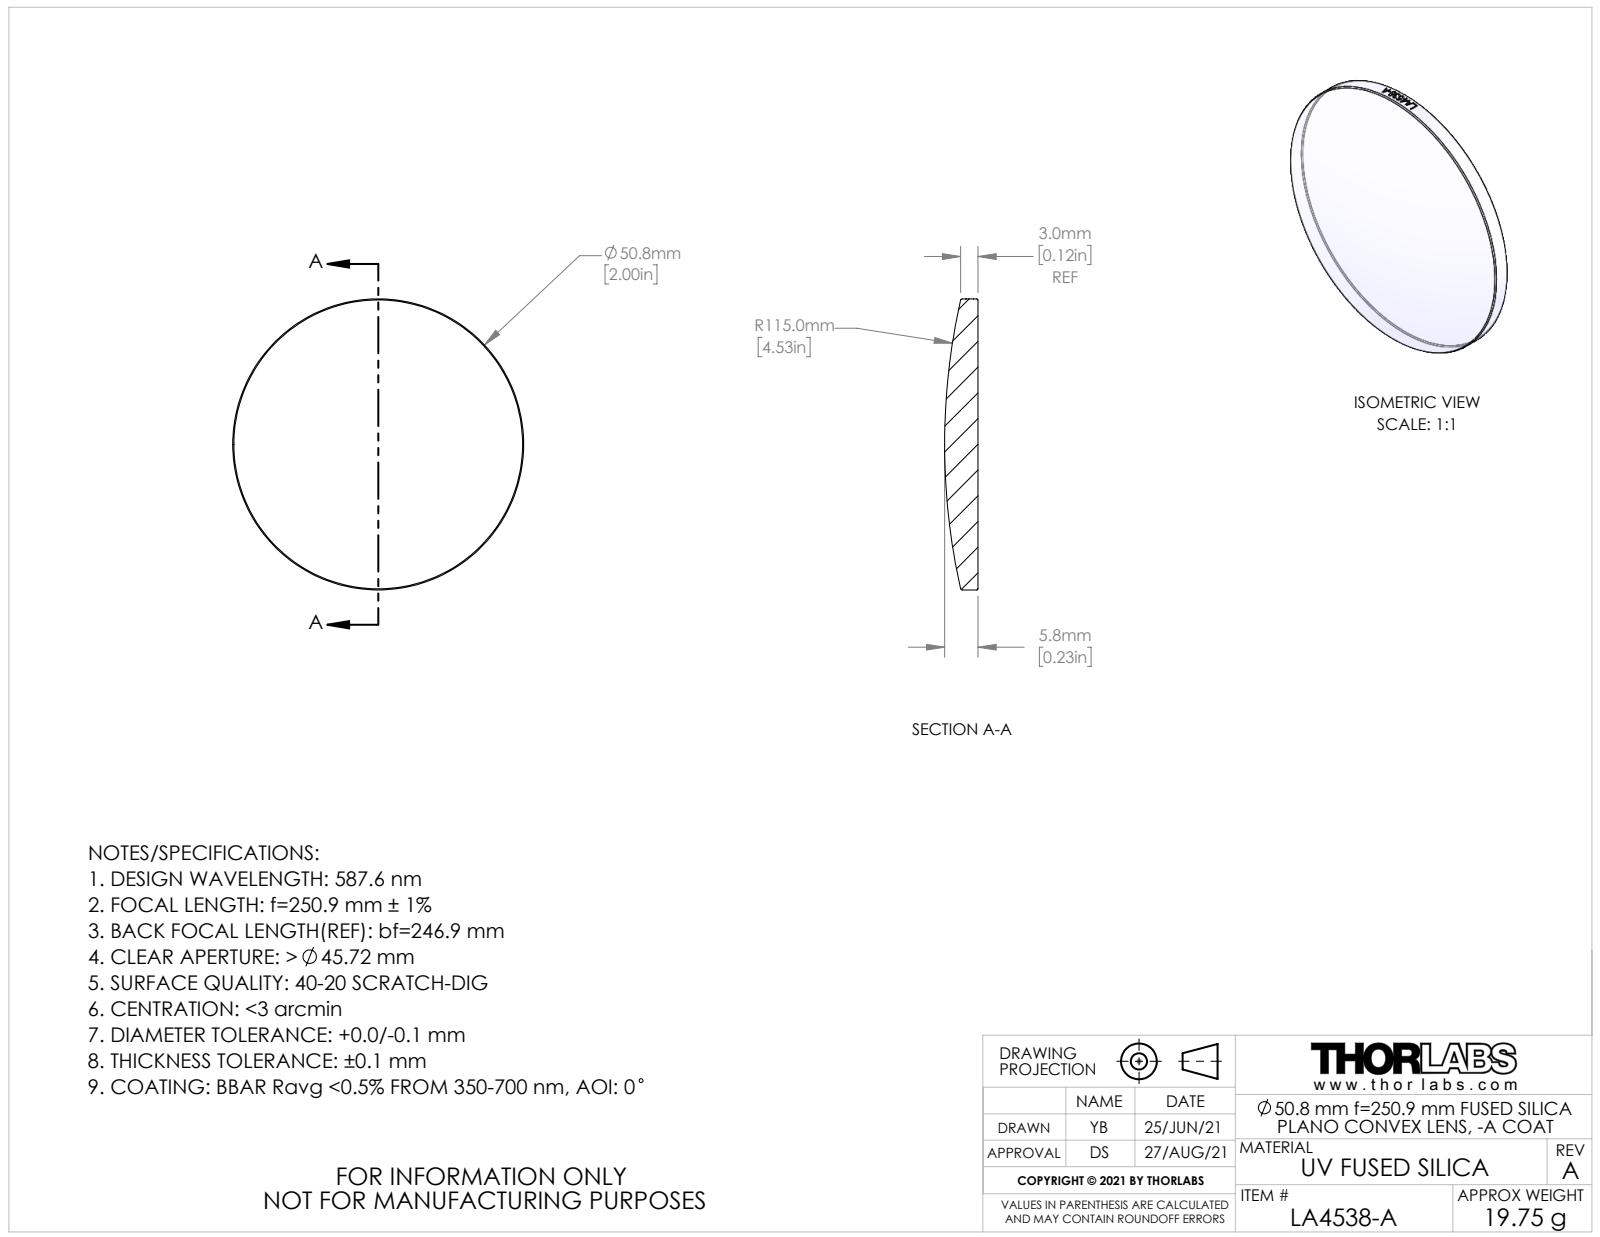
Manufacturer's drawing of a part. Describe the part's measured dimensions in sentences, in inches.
The part is named "CTN017568; CTN017540-E0W". Its 3-D file was written by "SolidWorks 2018 (AUTOMOTIVE_DESIGN)". It is 1 solid with 22 faces: 1 planar, 15 cylindrical and 6 other. Overall it measures 2 by 2 by 0.23 inches. Its volume is 0.547 cubic inches and its surface area 7.014 square inches. Round bosses or shafts: 1 of diameter 2.
